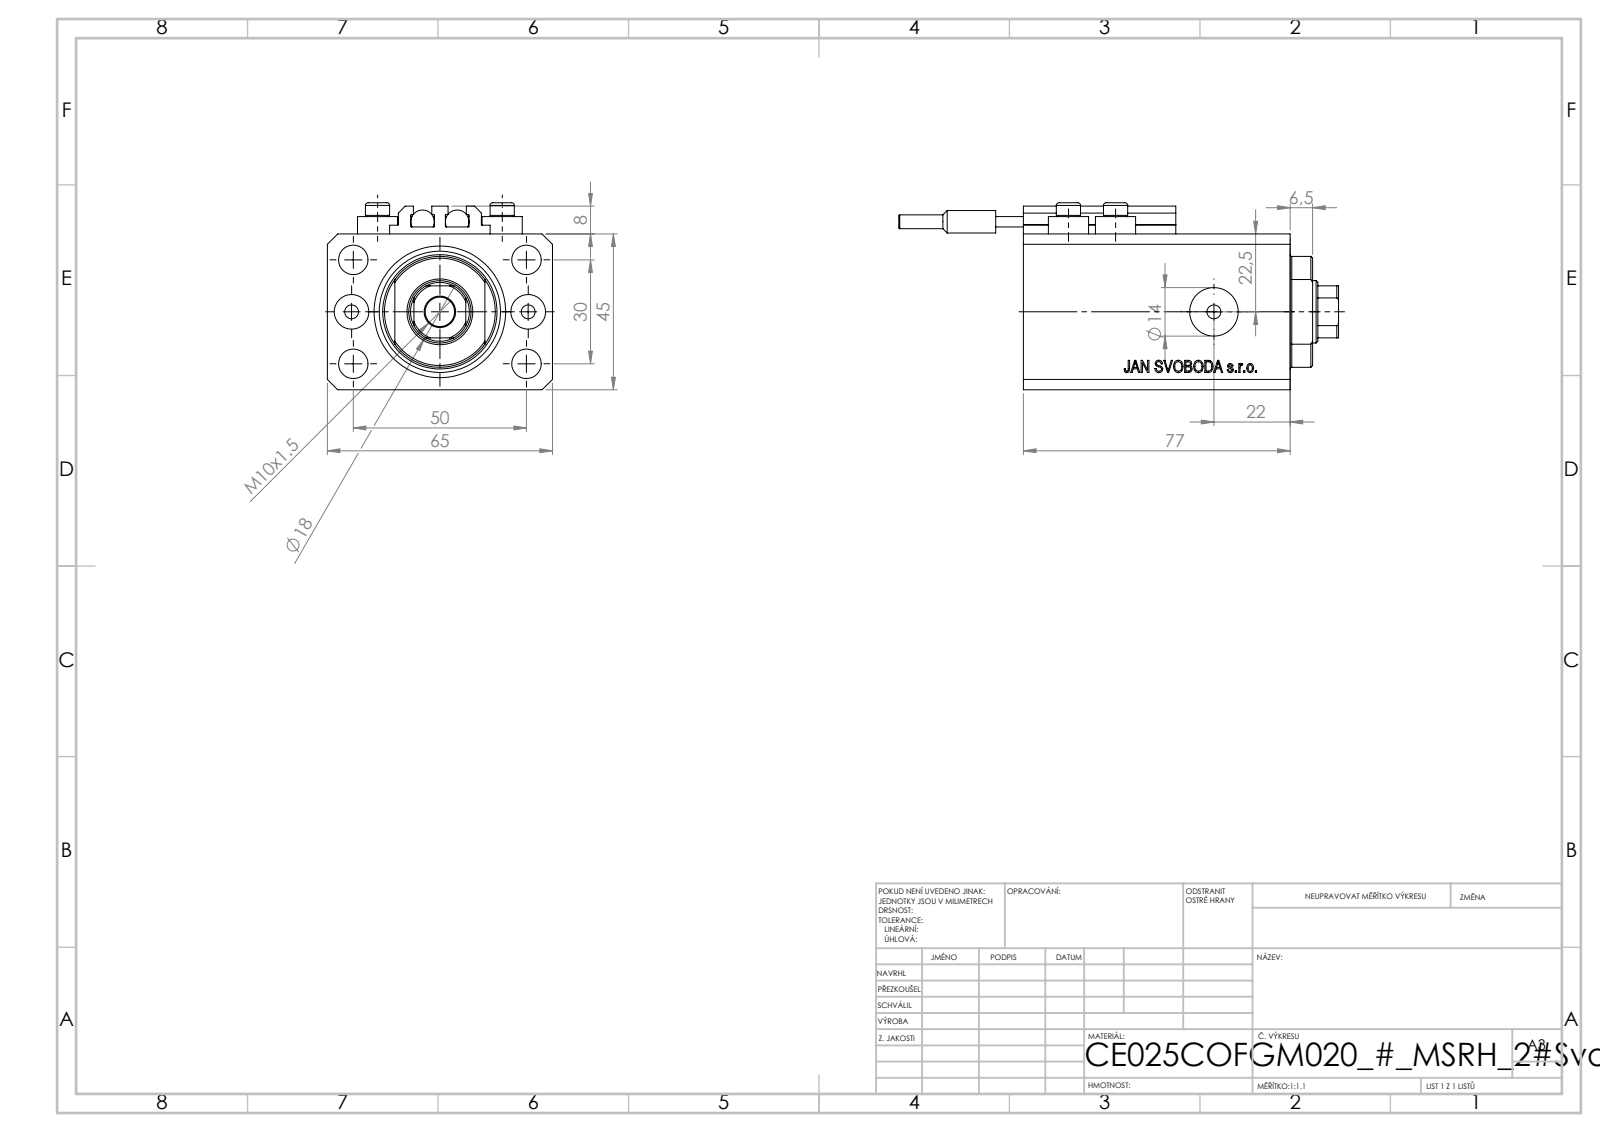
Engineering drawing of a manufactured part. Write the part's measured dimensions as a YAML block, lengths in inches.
part_name: "V250CE_VC_C; ALLEN BOLT V250CE; V250CE_C_Body; SWITCH_V250CE (+1 more)"
step_written_by: "SolidWorks 2019 (CONFIG_CONTROL_DESIGN)"
units: inches
bodies: {solids: 10, faces: 1086, planar: 536, cylindrical: 98, other: 452}
overall_size: [5, 2.559, 2.126]
volume: 13.15
surface_area: 93.02
round_holes:
  - {diameter: 0.157, count: 8}
  - {diameter: 0.335, count: 5}
  - {diameter: 0.394, count: 2}
  - {diameter: 0.551, count: 2}
  - {diameter: 0.709, count: 1}
  - {diameter: 0.984, count: 1}
  - {diameter: 1.496, count: 1}
round_bosses_or_shafts:
  - {diameter: 0.457, count: 4}
  - {diameter: 0.276, count: 4}
  - {diameter: 0.268, count: 2}
  - {diameter: 0.256, count: 2}
  - {diameter: 0.157, count: 2}
partial_cylinders:
  - {radius: 0.008, count: 10}
  - {radius: 0.335, count: 1}
  - {radius: 0.63, count: 1}
face_to_face_distances: [1.772, 2.559, 0.551, 2.48, 3.031, 0.118, 1.85, 0.272, 2.209, 2.76]
hole_center_spacings: [0.591, 1.148, 2.074, 0.535, 1.004, 1.181, 1.417, 1.515]
